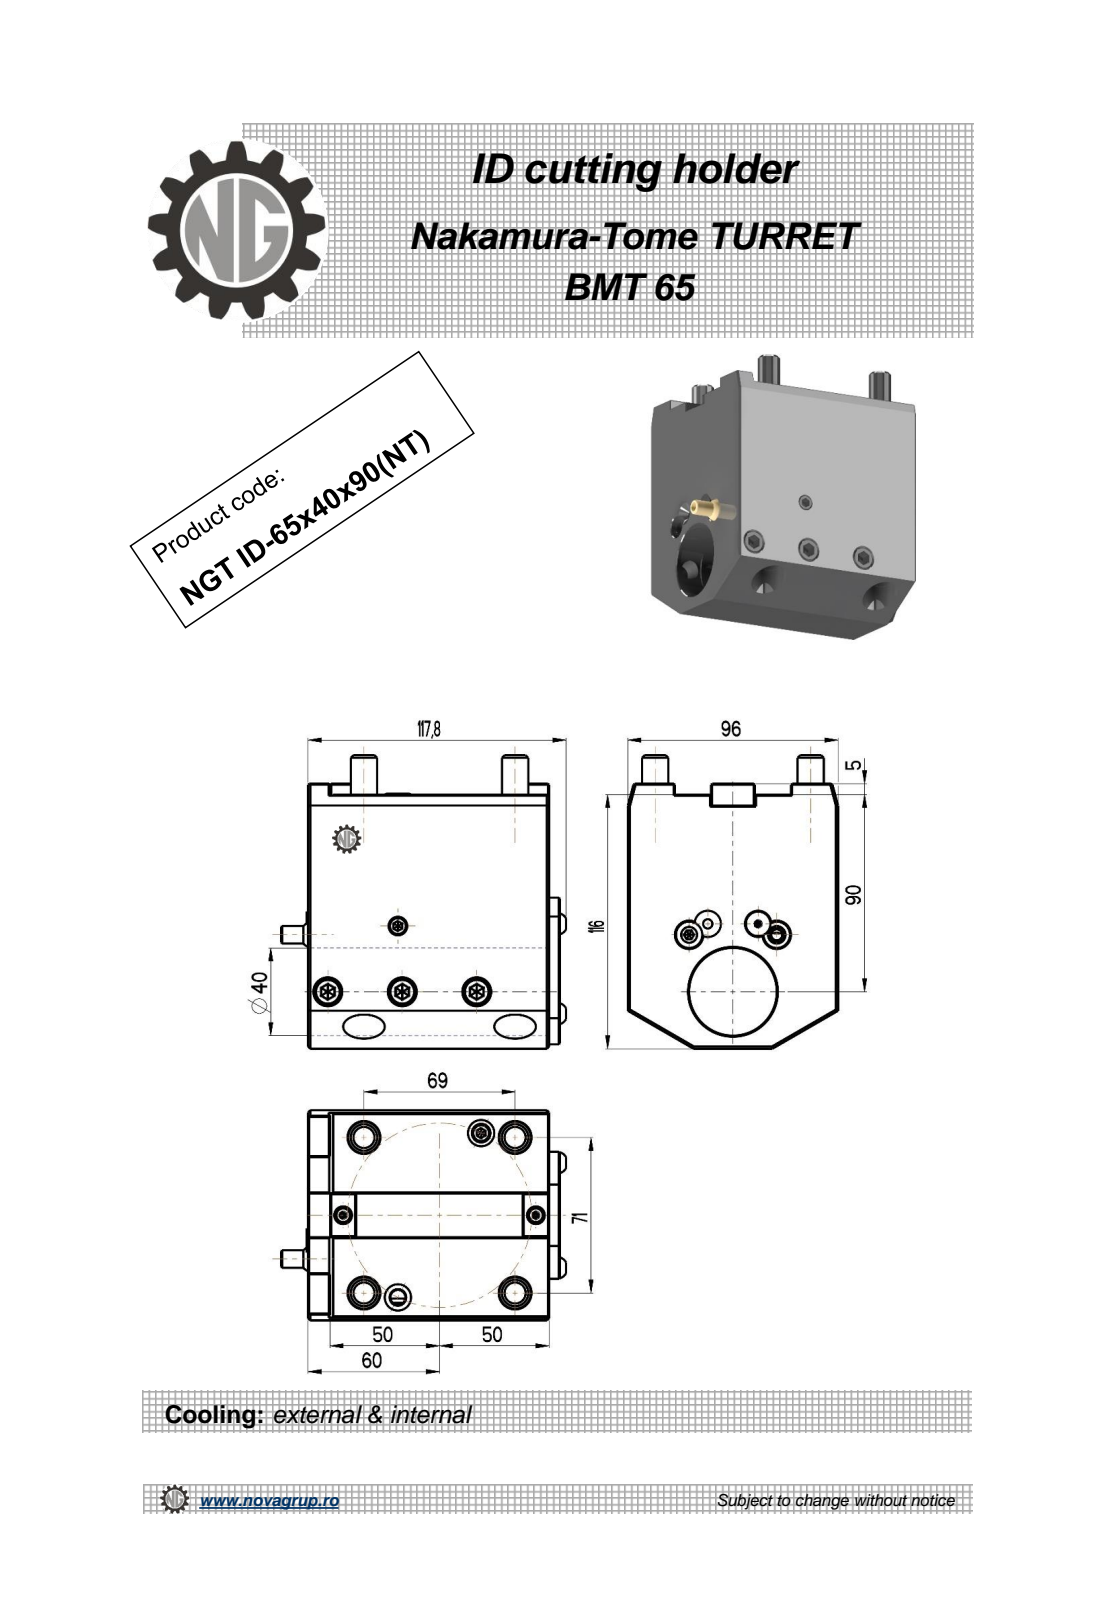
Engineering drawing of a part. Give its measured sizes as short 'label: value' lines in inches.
name: NGT_ID_65_40_90_NT
written by: PRO/ENGINEER BY PARAMETRIC TECHNOLOGY CORPORATION, 2010280 (CONFIG_CONTROL_DESIGN)
unit: in
bodies: 1 solid, 394 faces (213 planar, 83 cylindrical, 98 other)
size: 5.276 × 5.122 × 3.78
volume: 63.59 in³; area: 139 in²
holes: 3× ⌀0.402, 2× ⌀0.472, 1× ⌀0.197, 1× ⌀0.268, 1× ⌀1.575
bosses: 4× ⌀0.472, 1× ⌀0.441, 1× ⌀0.315
rounds: 36× R0.024, 6× R0.009, 6× R0.016
face distances: 3.78, 4.331, 0.197, 4.567, 4.528, 4.37, 2.283, 0.394, 1.496, 0.748
hole spacings: 1.339, 1.291, 2.677, 3.31
